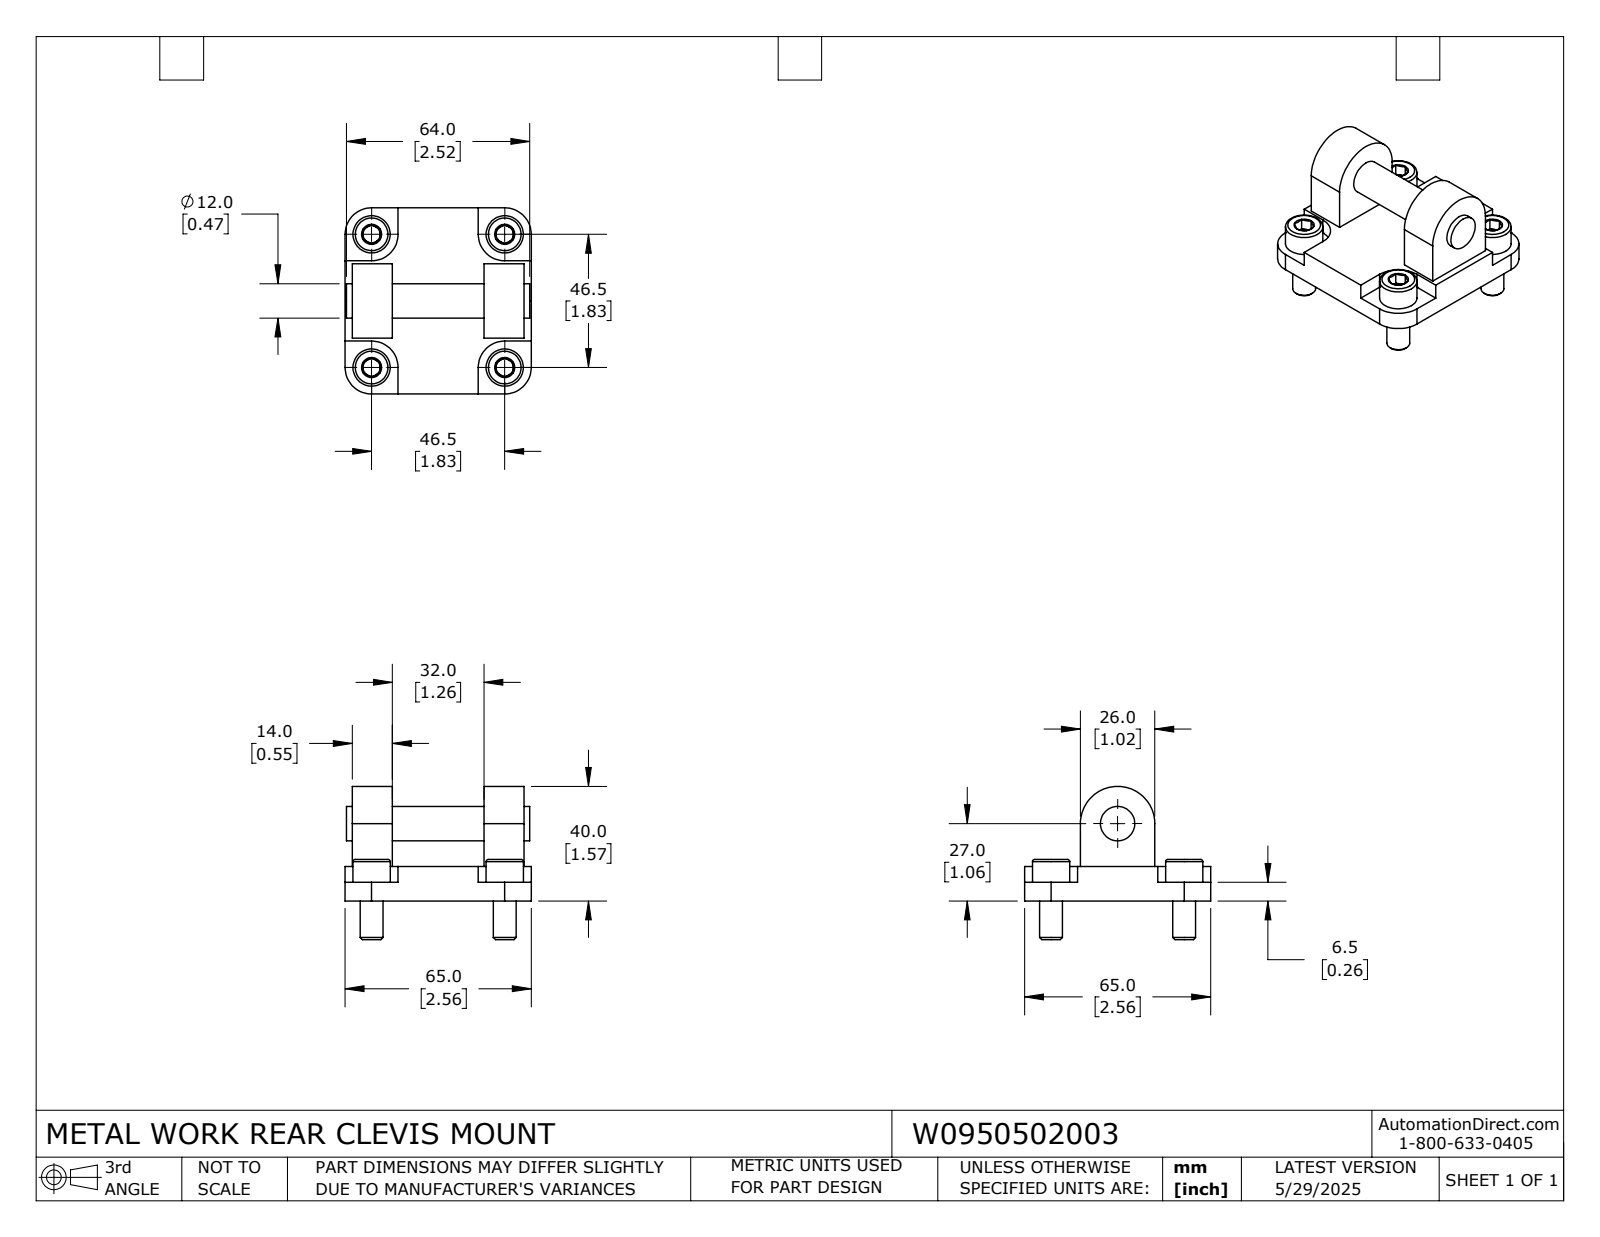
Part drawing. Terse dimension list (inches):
name: W0950502003
written by: SolidWorks 2024 (CONFIG_CONTROL_DESIGN)
unit: in
bodies: 5 solids, 187 faces (89 planar, 42 cylindrical, 56 other)
size: 2.559 × 2.559 × 2.106
volume: 3.829 in³; area: 33.99 in²
holes: 4× ⌀0.354, 1× ⌀1.575
bosses: 4× ⌀0.512, 4× ⌀0.315, 1× ⌀0.472
rounds: 4× R0.364, 1× R0.512
face distances: 0.472, 0.02, 1.811, 0.276, 0.197, 0.256, 0.217, 0.098, 0.551, 0.65
hole spacings: 1.294, 1.831, 2.589
